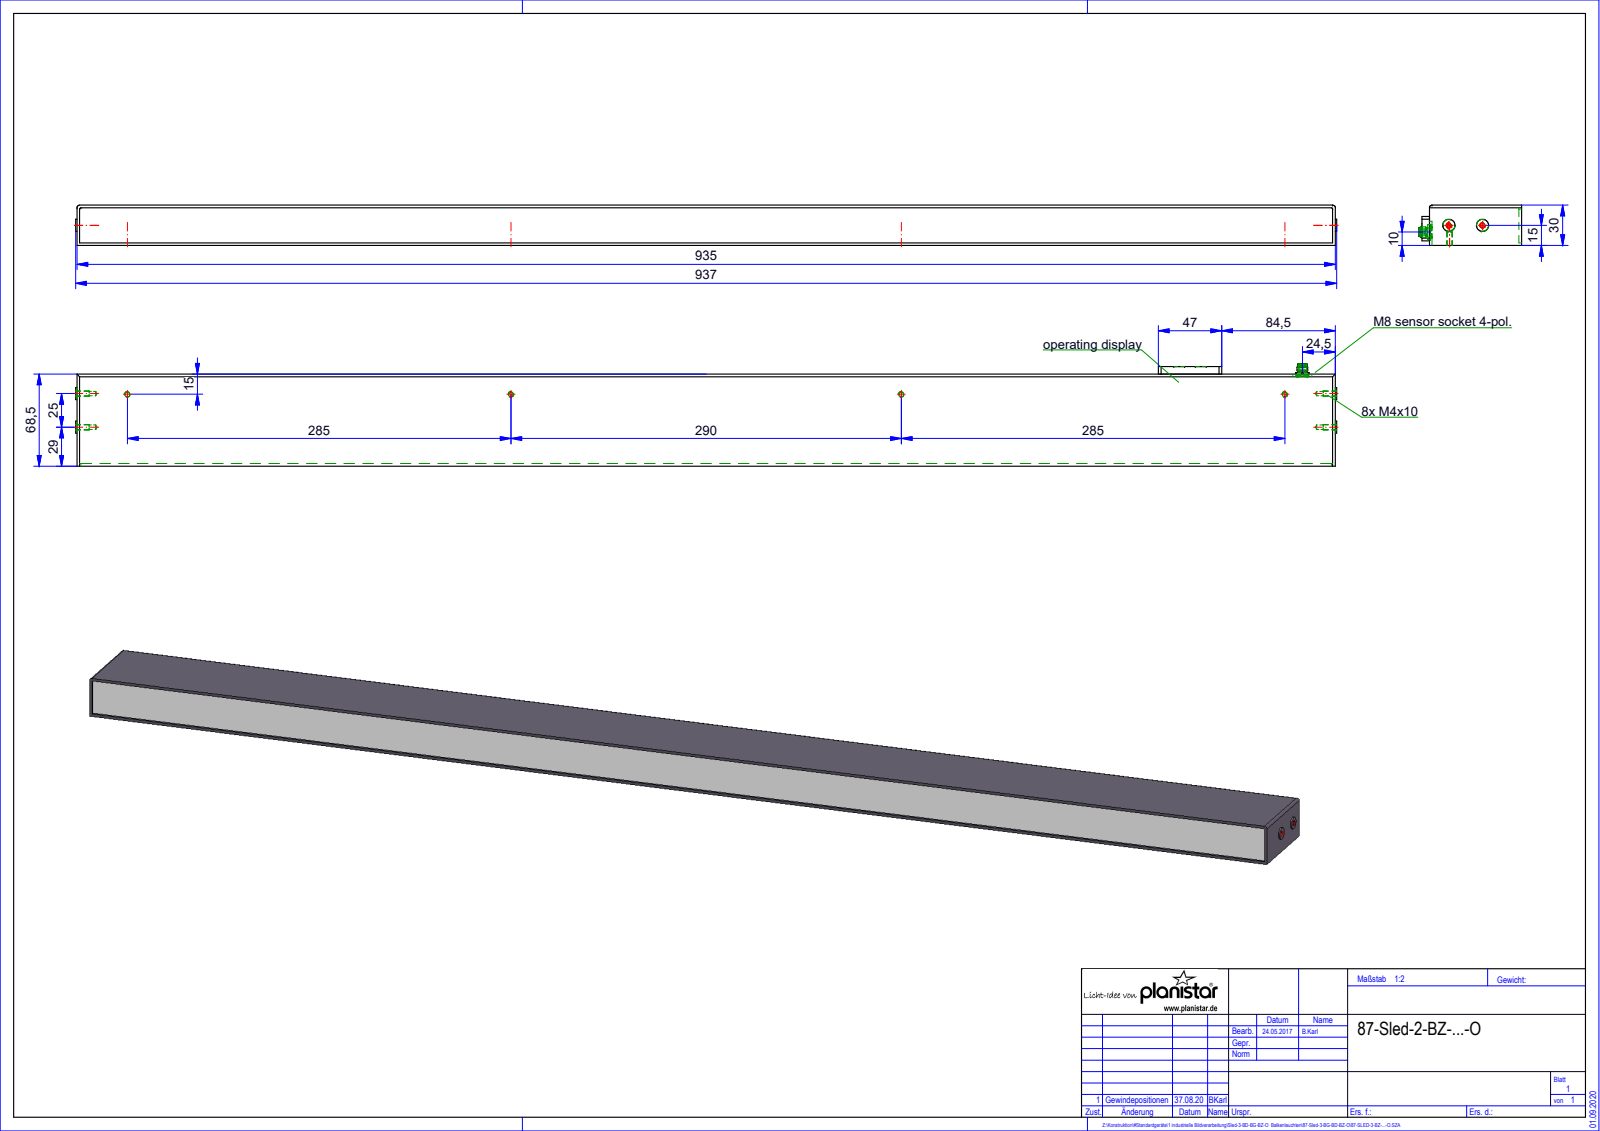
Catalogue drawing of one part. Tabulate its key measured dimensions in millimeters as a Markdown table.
| quantity | value |
| --- | --- |
| part name | Root; Baugruppe_Balkenleuchte; QUADER_3; 09-3391-00-04 (+1 more) |
| STEP written by | HiCAD 2015 2002.1 Build 408 (AUTOMOTIVE_DESIGN) |
| units | millimeters |
| bodies | 3 solids, 114 faces (47 planar, 50 cylindrical, 17 other) |
| overall size | 937 × 76.2 × 30 |
| volume | 1 876 000 mm³ |
| surface area | 195 835 mm² |
| round holes (diameter × count) | 3.3 × 6, 4 × 6, 5.8 × 1 |
| round bosses / shafts (diameter × count) | 1 × 4, 8 × 3, 9 × 2, 7.2 × 1, 6.8 × 1, 6.4 × 1 |
| partial cylindrical surfaces (radius × count) | 2 × 7, 1 × 2, 2.5 × 2, 5.5 × 1 |
| main face-to-face distances | 30, 66.5, 2, 68.5, 28, 26, 935, 74, 72, 5.5 |
| hole center spacings | 285, 575, 25, 290, 860 |
